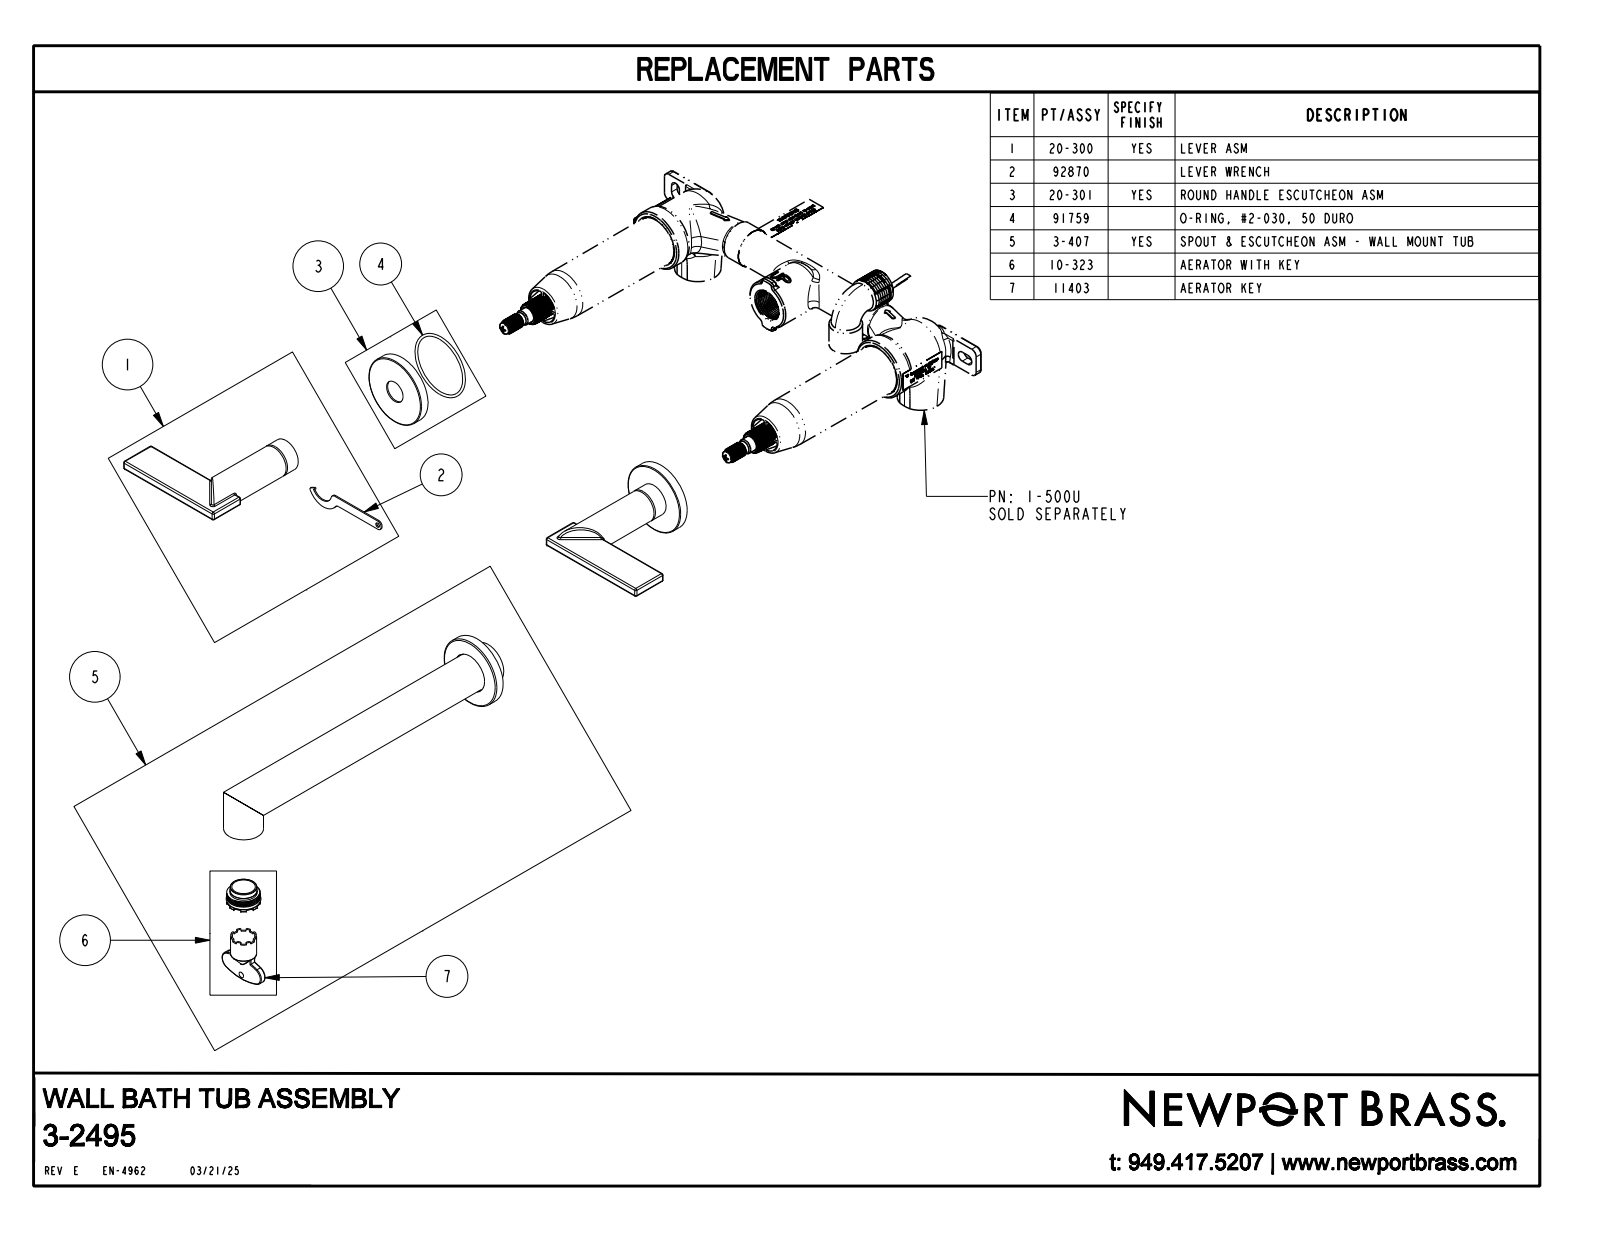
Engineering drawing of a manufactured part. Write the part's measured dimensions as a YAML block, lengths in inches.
part_name: "3-2495_SW0001"
step_written_by: "CREO PARAMETRIC BY PTC INC, 2018400 (AUTOMOTIVE_DESIGN)"
units: inches
bodies: {solids: 3, faces: 141, planar: 31, cylindrical: 58, other: 52}
overall_size: [12.995, 8.75, 7.8]
volume: 13.16
surface_area: 76.23
round_bosses_or_shafts:
  - {diameter: 1.85, count: 2}
  - {diameter: 1, count: 2}
  - {diameter: 0.86, count: 2}
  - {diameter: 0.68, count: 2}
  - {diameter: 1.75, count: 1}
partial_cylinders:
  - {radius: 0.04, count: 28}
face_to_face_distances: [0.25, 0.236, 3.45, 3.2, 6.633, 6.87, 2.466, 2.216, 0.984, 0.676]
